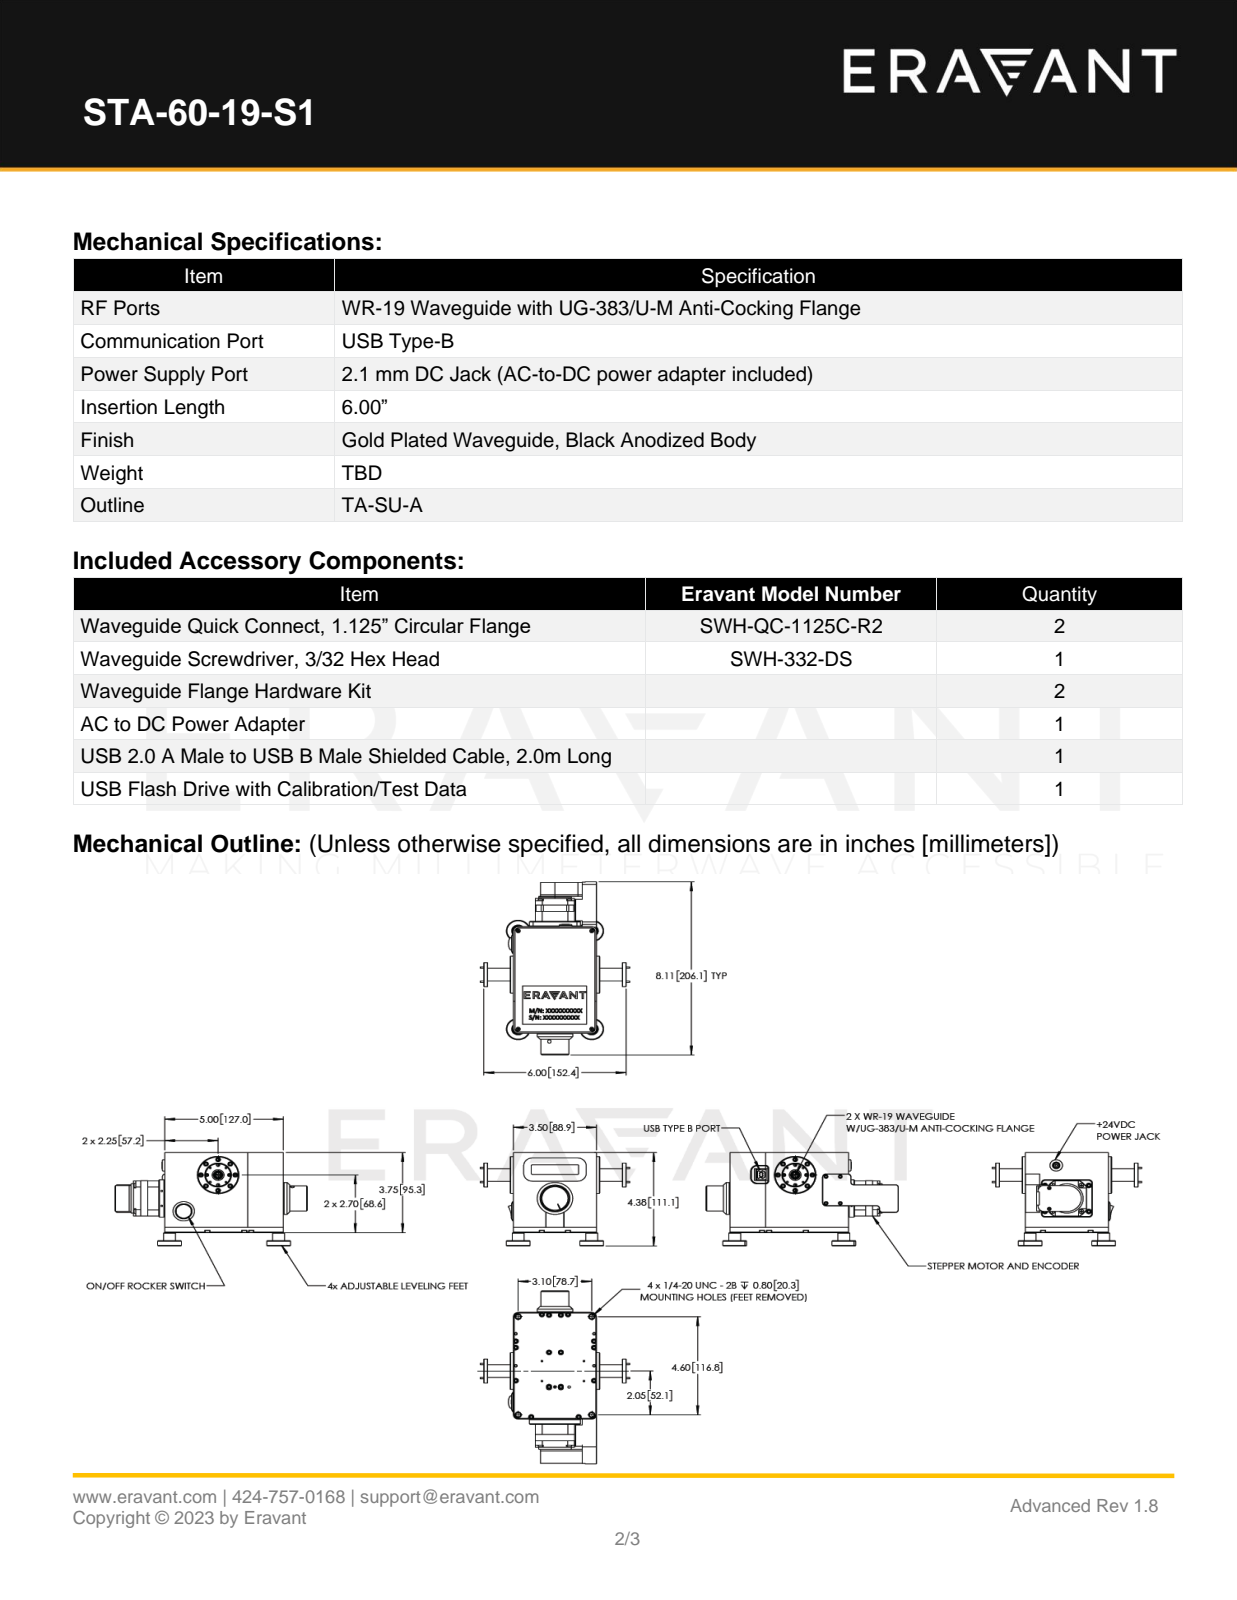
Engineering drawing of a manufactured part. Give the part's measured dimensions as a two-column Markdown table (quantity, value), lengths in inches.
| quantity | value |
| --- | --- |
| part name | STA-60-19-S1 |
| STEP written by | SolidWorks 2021 (CONFIG_CONTROL_DESIGN) |
| units | inches |
| bodies | 58 solids, 3081 faces (1329 planar, 894 cylindrical, 858 other) |
| overall size | 8.114 × 6.305 × 4.375 |
| volume | 35.41 in³ |
| surface area | 339.1 in² |
| round holes (diameter × count) | 0.089 × 20, 0.07 × 18, 0.129 × 18, 0.096 × 12, 0.2 × 9, 0.219 × 8, 0.061 × 4, 0.067 × 4, 0.097 × 4, 0.118 × 4, 0.14 × 4, 0.144 × 4 |
| round bosses / shafts (diameter × count) | 0.183 × 29, 0.112 × 24, 0.086 × 8, 0.5 × 5, 1 × 4, 0.25 × 4, 0.205 × 4, 0.14 × 4 |
| partial cylindrical surfaces (radius × count) | 0.012 × 44, 0.25 × 24, 0.024 × 14, 0.109 × 14, 0.15 × 14, 0.125 × 13, 0.158 × 8, 0.015 × 6 |
| main face-to-face distances | 3.5, 0.25, 0.2, 3.3, 3.75, 3.437, 0.063, 3.687, 5, 3.1 |
| hole center spacings | 0.515, 1.107, 0.863, 1.025, 0.359, 0.469, 0.663, 0.866 |
